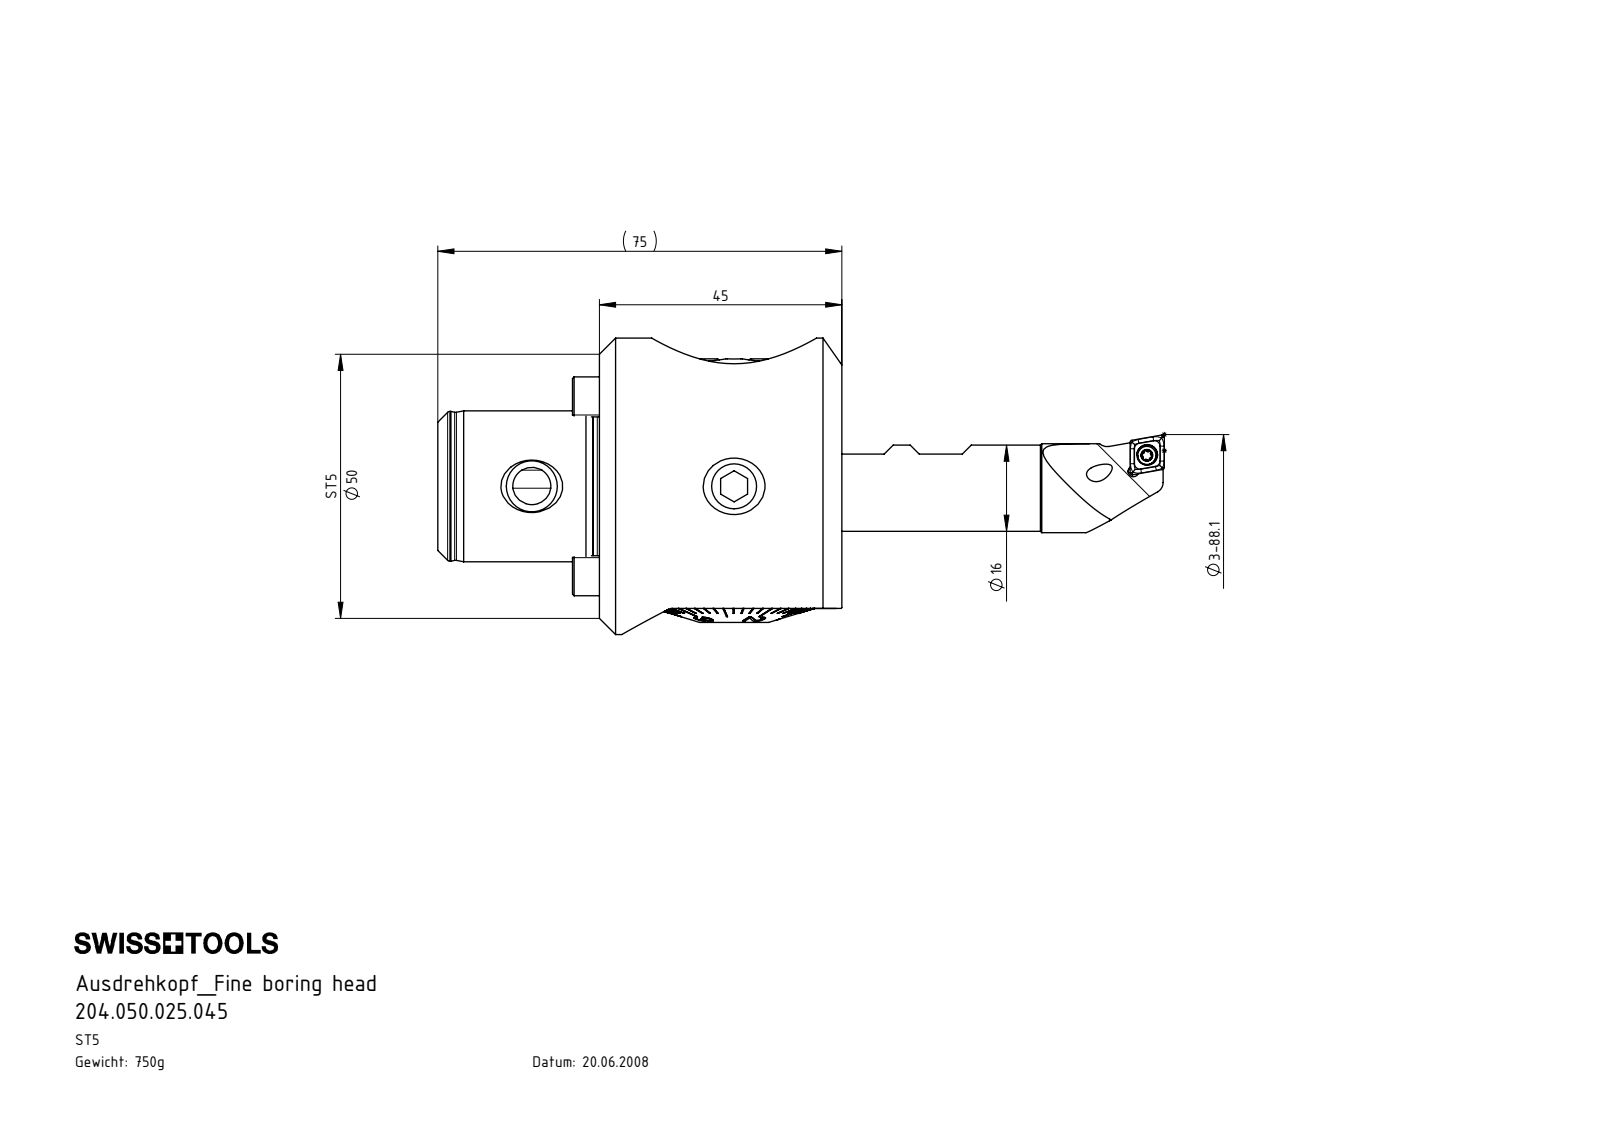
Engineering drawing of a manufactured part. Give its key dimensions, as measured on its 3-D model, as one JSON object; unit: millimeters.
{"part_name": "A55-BG1.DA3.041_A; ISO 4026 - M10 x 16_PreviewCfg; DIN 3771 - 25x1.5; ST5-A55.AA3.045_A_Fertigbearbeitung (+8 more)", "step_written_by": "SolidWorks 2017 (AUTOMOTIVE_DESIGN)", "units": "millimeters", "bodies": {"solids": 16, "faces": 609, "planar": 319, "cylindrical": 91, "other": 199}, "overall_size": [75, 55, 55], "volume_mm3": 93564, "surface_area_mm2": 37546, "round_holes": [[8.5, 3], [4, 2], [1.6, 1], [3.3, 1], [4.2, 1], [8, 1], [10, 1], [11.4, 1], [12.4, 1], [14, 1], [14.2, 1], [16, 1]], "round_bosses_or_shafts": [[10, 3], [5, 2], [55, 1], [30, 1], [29.98, 1], [29.9, 1], [28, 1], [27.8, 1]], "partial_cylinders_radius": [[0.34, 6], [0.59, 6], [0.5, 4], [1.4, 4], [1.9, 4], [3.2, 3], [2, 2], [5.47, 2]], "face_to_face_distances": [45, 5.3, 2.8, 2.5, 6.5, 3.7, 1.2, 5.2, 5, 7], "hole_center_spacings": [7.25, 14.5, 22.27, 8.5, 16.55, 17.25, 19.14, 28.48]}
